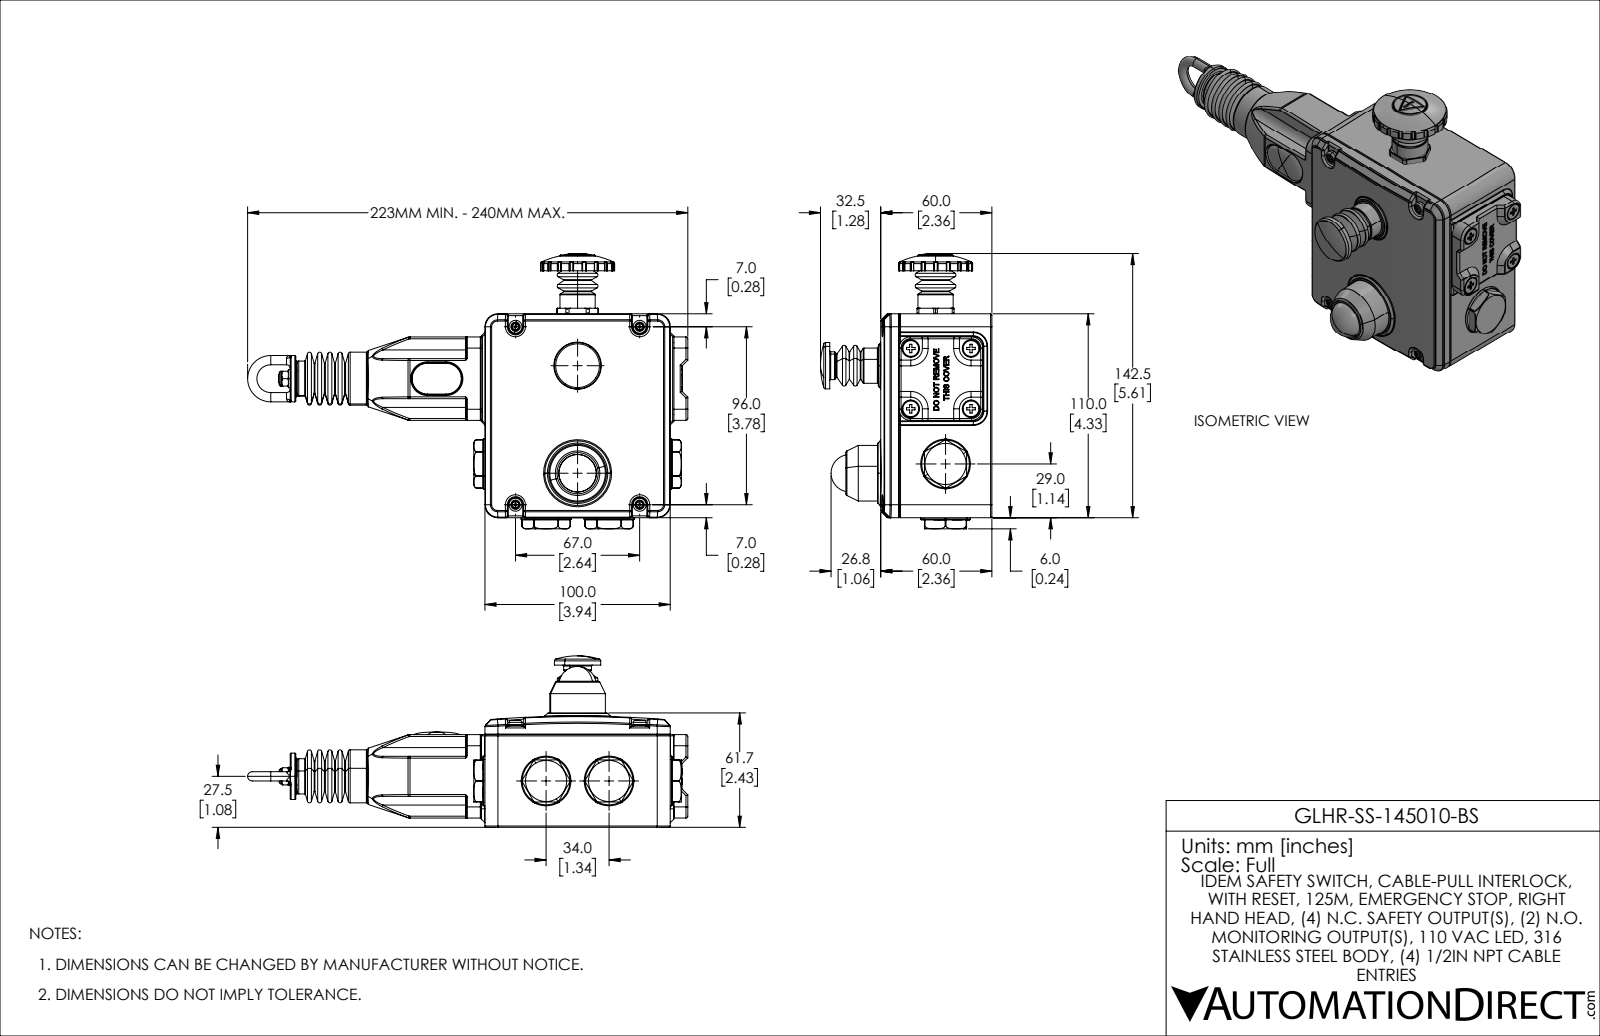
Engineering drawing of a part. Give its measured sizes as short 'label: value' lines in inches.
name: GLHR-SS-145010-BS
written by: SolidWorks 2021 (AUTOMOTIVE_DESIGN)
unit: in
bodies: 47 solids, 4430 faces (1376 planar, 1434 cylindrical, 1620 other)
size: 9.374 × 5.775 × 3.654
volume: 19.04 in³; area: 299.7 in²
holes: 9× ⌀0.197, 9× ⌀0.209, 8× ⌀0.378, 7× ⌀0.161, 6× ⌀0.354, 4× ⌀0.13, 4× ⌀0.157, 4× ⌀0.189, 4× ⌀0.213, 4× ⌀0.228, 3× ⌀0.067, 3× ⌀0.102
bosses: 11× ⌀0.197, 8× ⌀0.335, 8× ⌀0.173, 5× ⌀0.276, 4× ⌀0.787, 4× ⌀0.138, 4× ⌀0.051, 3× ⌀0.945
rounds: 221× R0.02, 164× R0.039, 76× R0.008, 48× R0.028, 18× R0.012, 14× R0.006, 14× R0.079, 10× R0.004
face distances: 0.039, 0.079, 0.138, 2.181, 0.114, 2.067, 4.016, 0.157, 4.331, 0.335
hole spacings: 1.28, 1.28, 0.905, 0.374, 0.228, 0.902, 0.906, 0.907
